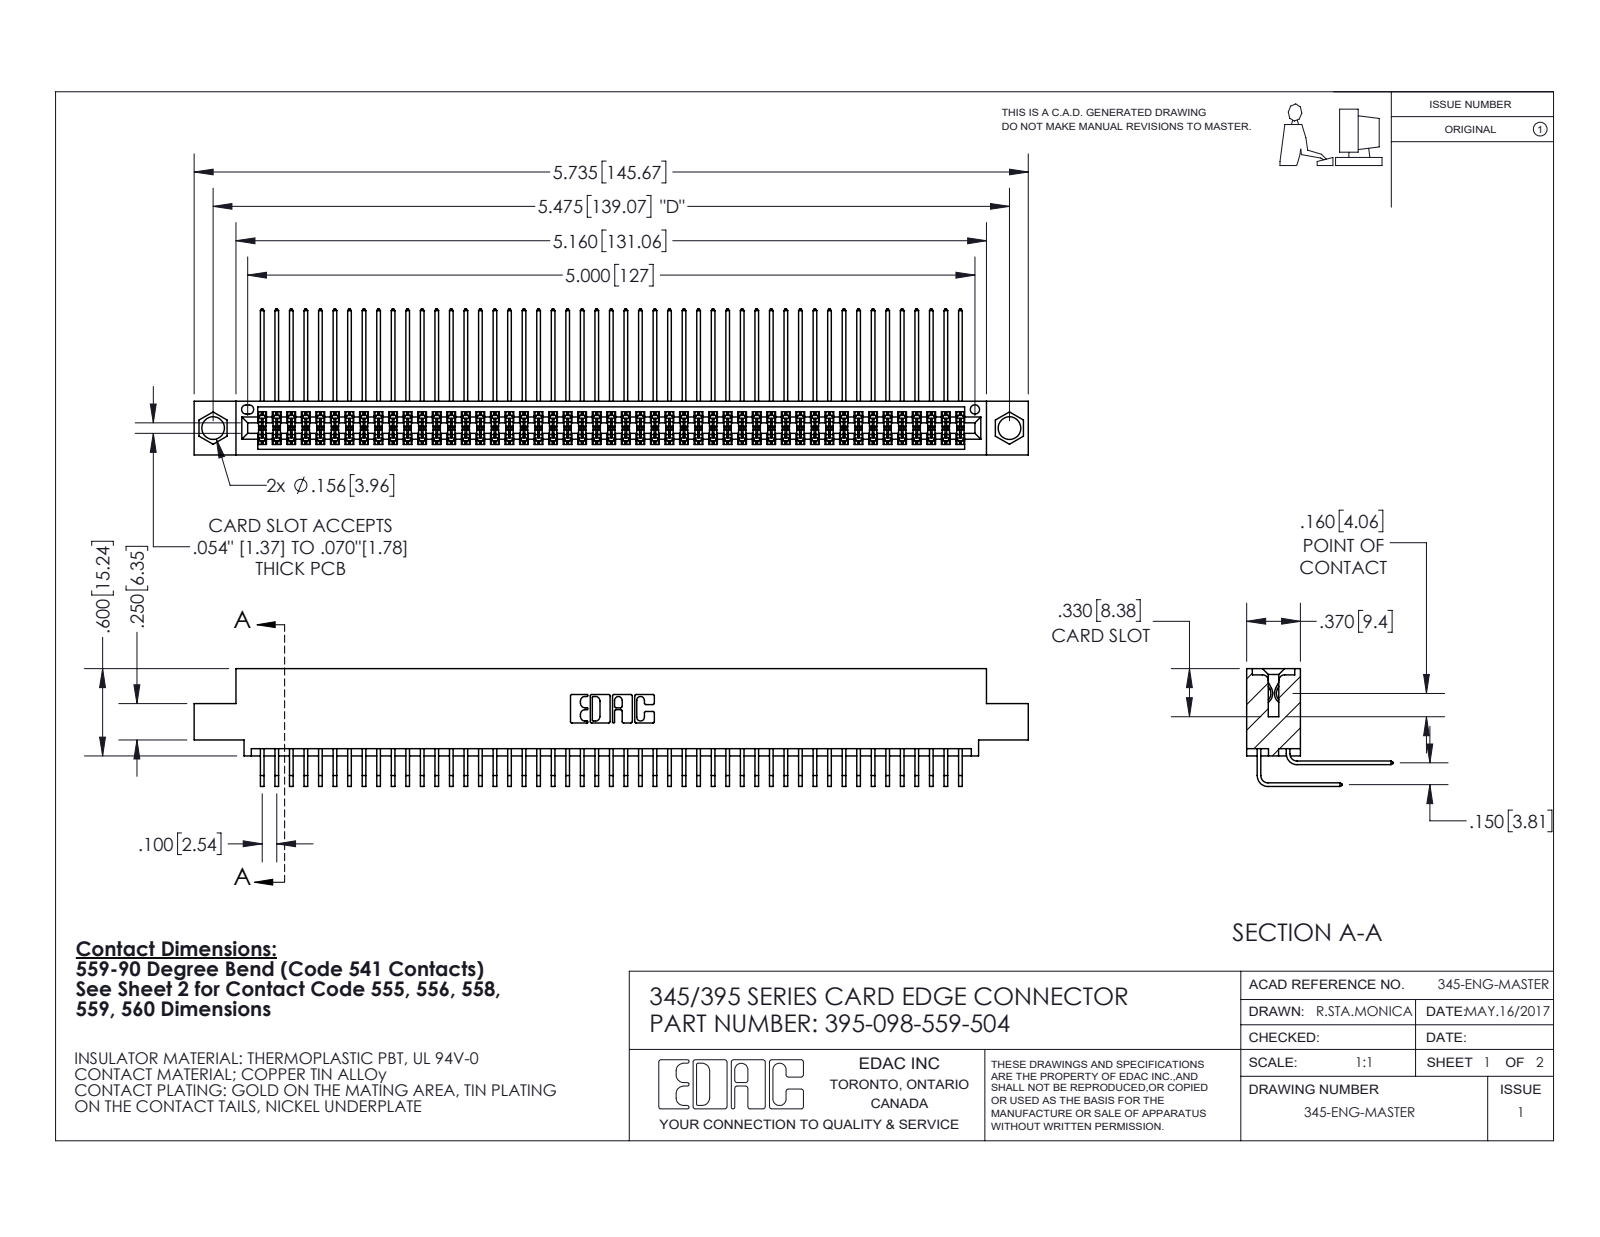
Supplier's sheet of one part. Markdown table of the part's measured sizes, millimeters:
| quantity | value |
| --- | --- |
| part name | 395-098-559-504; 345-292-001_558 559 Tail - 1; 345 Part_0.110 Offset - 0.156 Dia-TI; 345-292-001_559 Tail - 2 |
| STEP written by | SolidWorks 2020 (CONFIG_CONTROL_DESIGN) |
| units | millimeters |
| bodies | 99 solids, 5240 faces (3528 planar, 1712 cylindrical, 0 other) |
| overall size | 145.7 × 25.5 × 20.5 |
| volume | 14 600 mm³ |
| surface area | 24 320 mm² |
| round holes (diameter × count) | 4 × 2, 1.6 × 1 |
| partial cylindrical surfaces (radius × count) | 0.2 × 196, 0.3 × 22, 0.2 × 6, 0.8 × 6, 0.7 × 3, 0.4 × 2, 0.5 × 2, 0.6 × 2 |
| main face-to-face distances | 1.8, 7.6, 5.1, 9.4, 2.5, 6.9, 0.6, 5.7, 4.4, 3.8 |
| hole center spacings | 6.9, 133.1, 139.1 |
